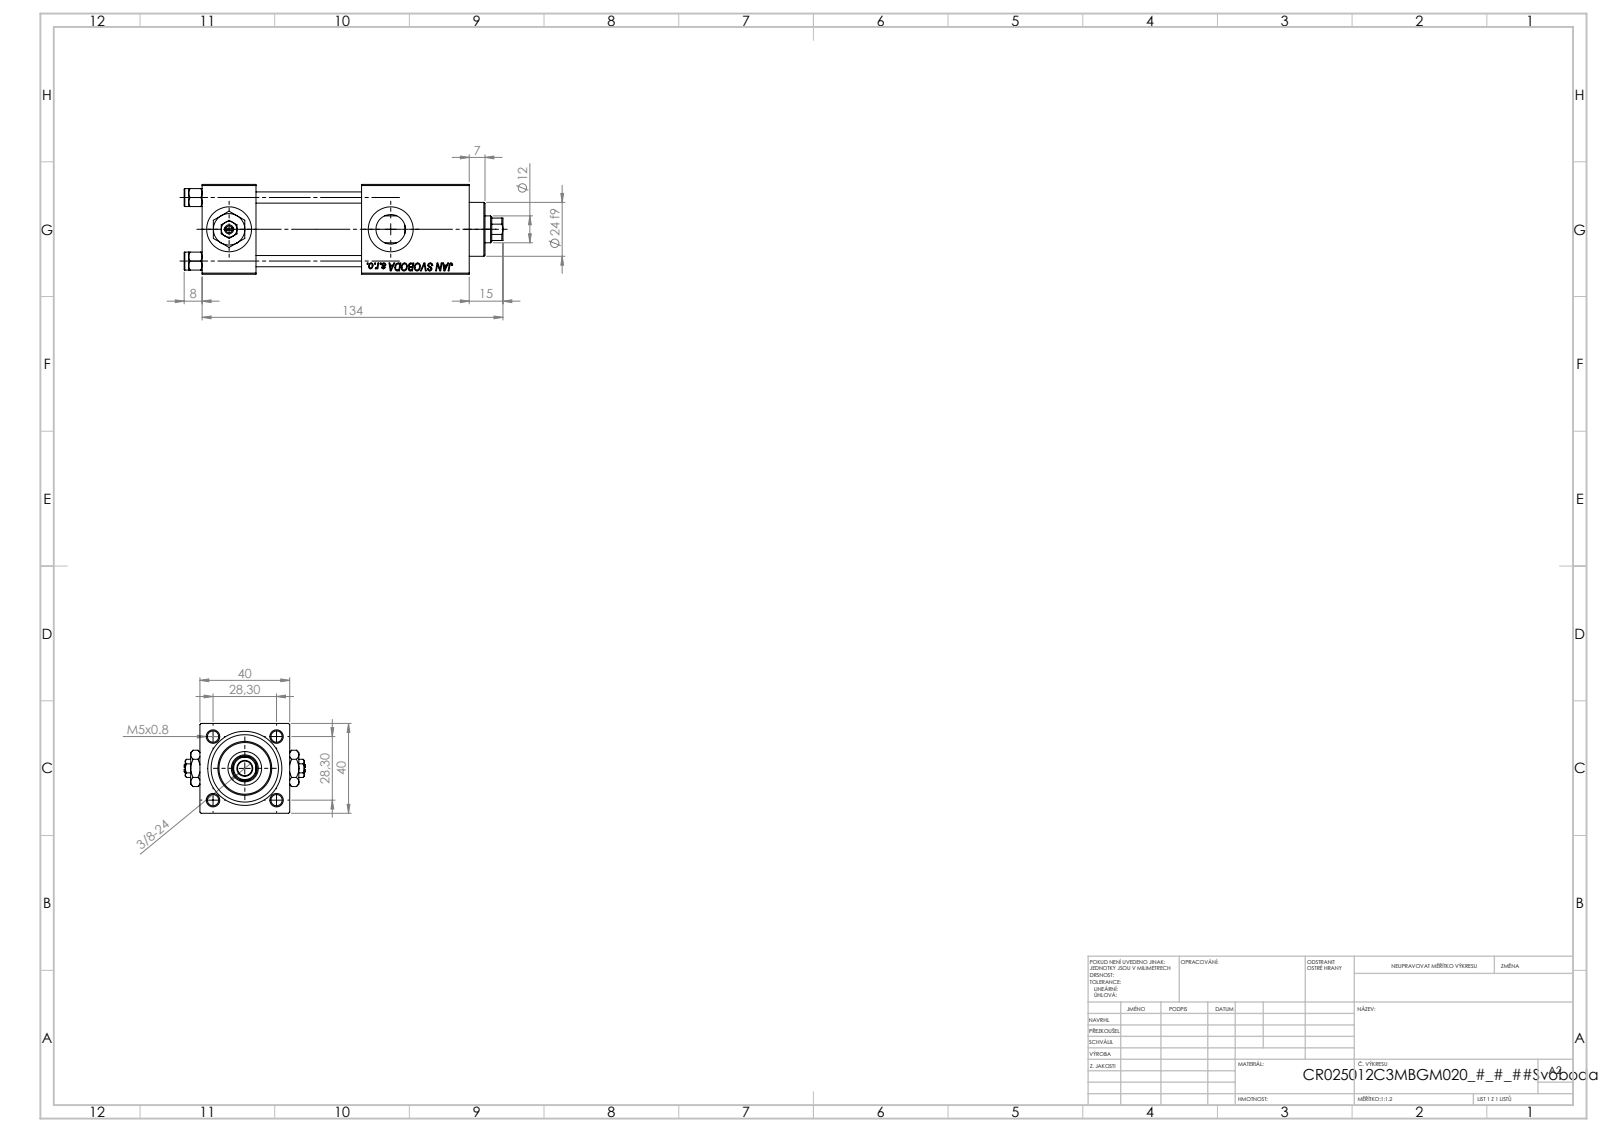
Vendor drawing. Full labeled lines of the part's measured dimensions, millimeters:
Part name (STEP PRODUCT): V215CR_C_TYCINKA; NUT_M5_C; V215_VC_A; V215CR_VCP_C (+2 more)
STEP written by: SolidWorks 2019 (CONFIG_CONTROL_DESIGN)
Units: millimetres
Bodies: 13 solids, 1248 faces (572 planar, 98 cylindrical, 578 other)
Overall size (bounding box): 142 × 54 × 40
Volume: 140 985 mm³ · Surface area: 56 209 mm²
Round holes (diameter × count): ⌀5 ×4, ⌀20 ×3, ⌀7 ×2, ⌀13.16 ×2, ⌀6.5 ×1, ⌀12 ×1, ⌀15 ×1, ⌀25 ×1, ⌀30 ×1
Round bosses / shafts (diameter × count): ⌀8 ×4, ⌀31 ×1, ⌀24 ×1
Partial cylindrical surfaces — rounded edges, fillets, slot ends (radius × count): R5.5 ×1
Main face-to-face distances: 40, 24, 39.8, 90.3, 66.3, 48, 47, 71, 19.3, 119
Hole centre spacings: 20.01, 28.3, 40.02, 72
